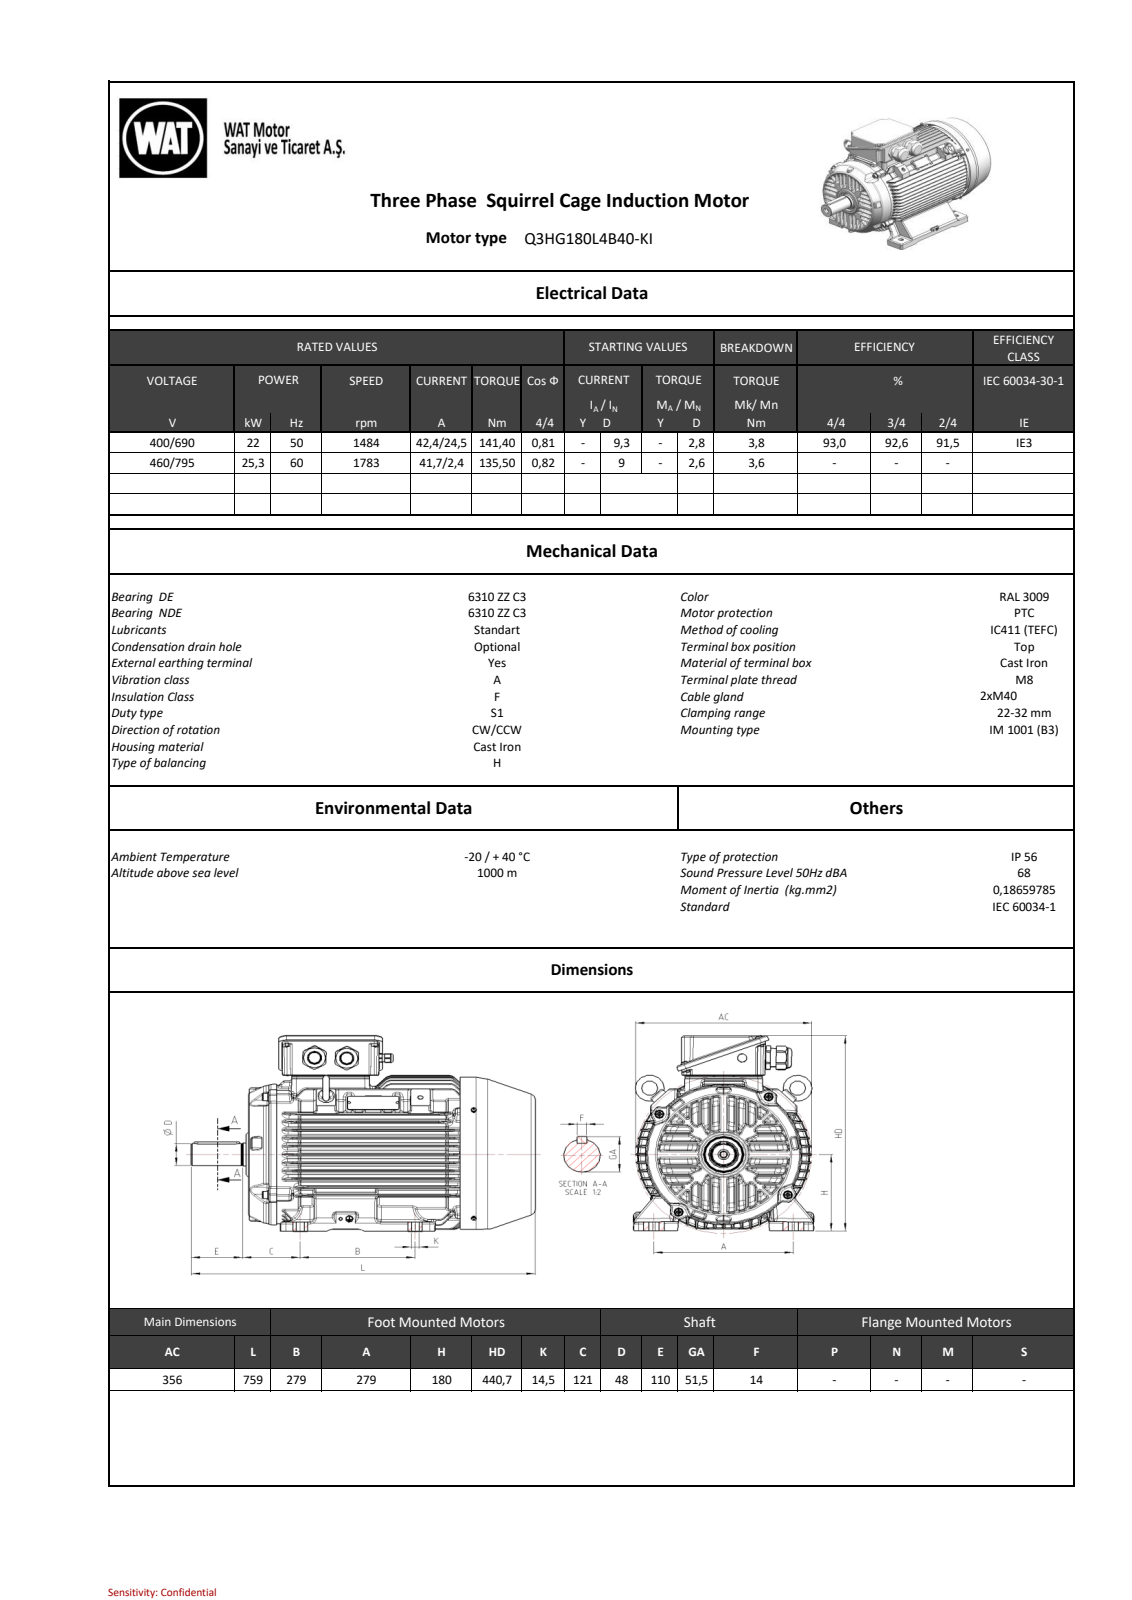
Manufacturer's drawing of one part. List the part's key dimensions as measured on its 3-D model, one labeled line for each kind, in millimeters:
Part name (STEP PRODUCT): C901598425C53z9j
STEP written by: SIEMENS PLM Software NX 11.0 (AUTOMOTIVE_DESIGN)
Units: millimetres
Bodies: 0 solids, 7391 faces (2132 planar, 1547 cylindrical, 3712 other)
Overall size (bounding box): 762.5 × 440.73 × 355.28
Round holes (diameter × count): ⌀9 ×8, ⌀2.5 ×2, ⌀10.9 ×2, ⌀6.8 ×1, ⌀8 ×1, ⌀14 ×1, ⌀17 ×1, ⌀75.8 ×1, ⌀76 ×1, ⌀343.6 ×1
Round bosses / shafts (diameter × count): ⌀16 ×8, ⌀12 ×7, ⌀20 ×4, ⌀46 ×2, ⌀42.2 ×2, ⌀30 ×2, ⌀346 ×1, ⌀310 ×1
Partial cylindrical surfaces — rounded edges, fillets, slot ends (radius × count): R4 ×360, R3 ×192, R1.5 ×136, R2 ×107, R5 ×66, R1.8 ×48, R0.4 ×24, R10 ×21
Main face-to-face distances: 14.54, 14.46, 29, 29.14, 14.6, 43.6, 58.71, 58.25, 43.79, 29.25
Hole centre spacings: 223.45, 54.7, 158, 158.01, 181.4, 258.76, 311.24, 316.01
